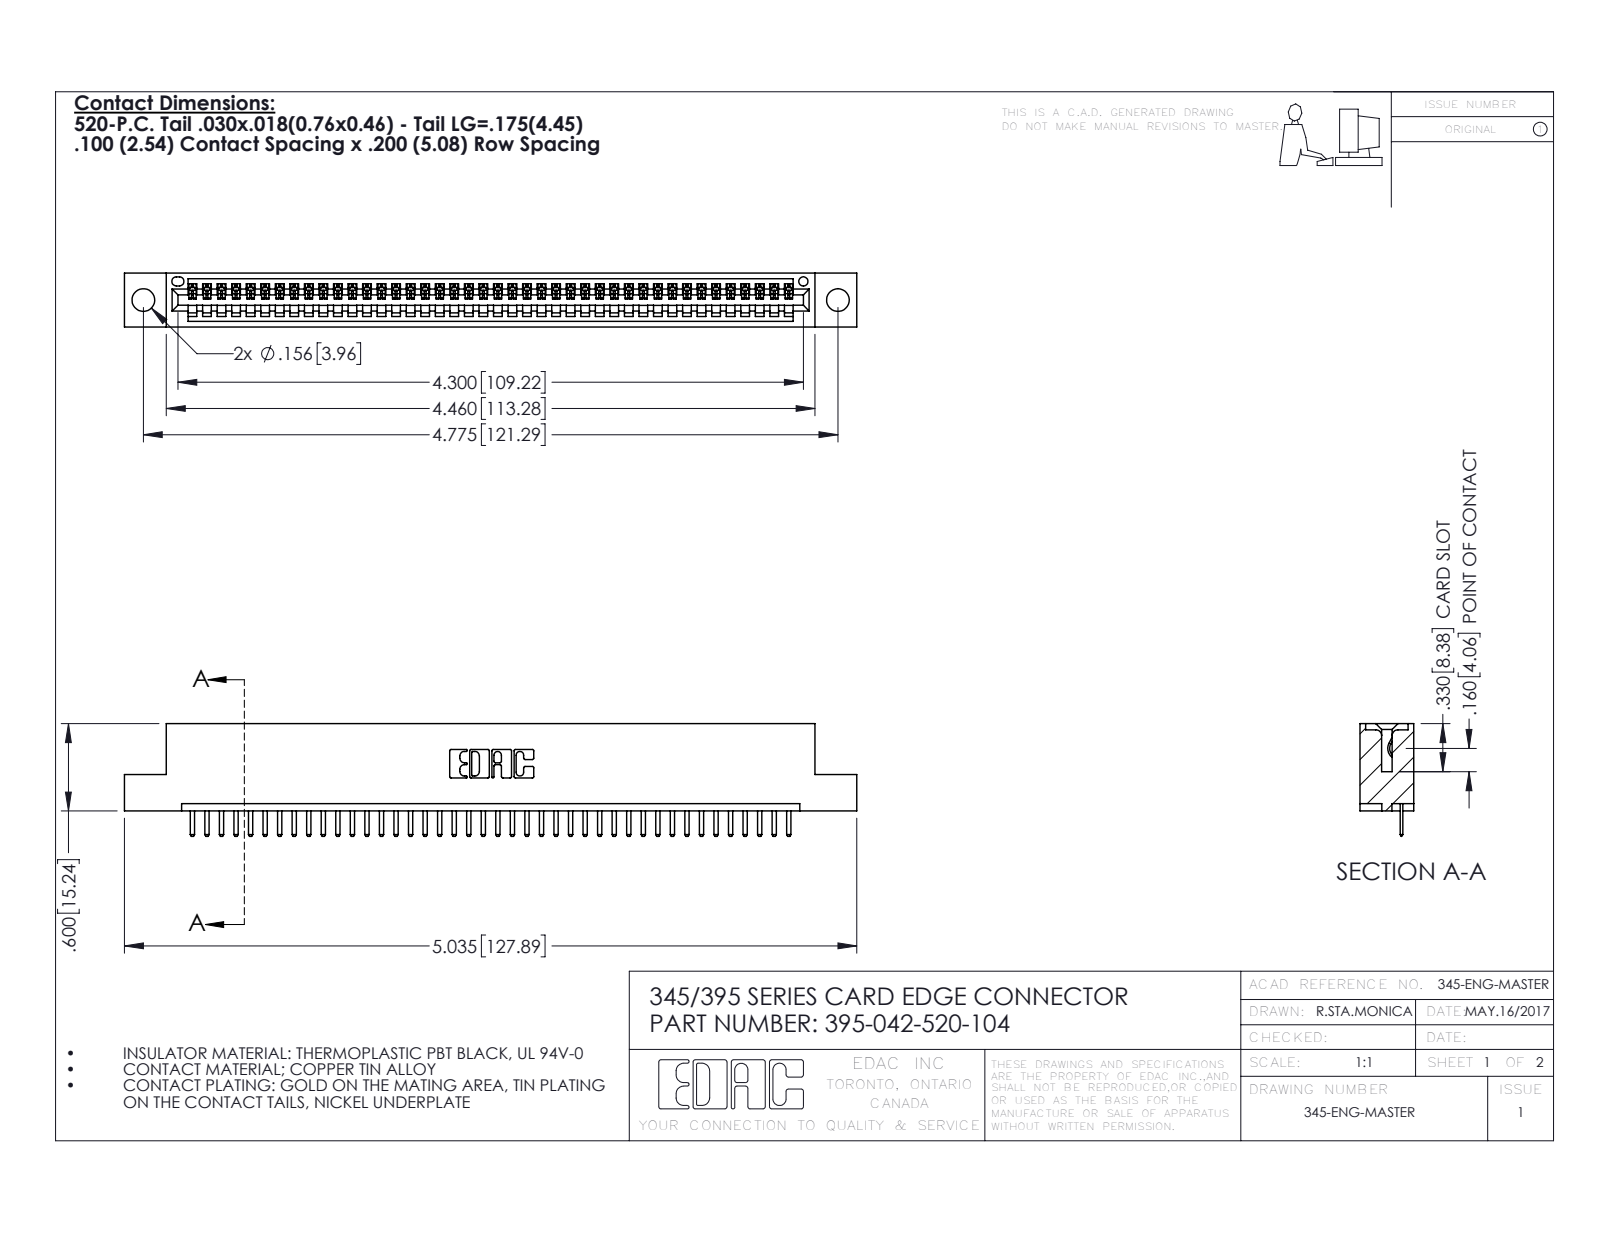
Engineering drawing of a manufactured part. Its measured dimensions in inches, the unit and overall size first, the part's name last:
Units: inches
Overall size (bounding box): 5.035 × 0.775 × 0.37
Round holes (diameter × count): ⌀0.156 ×2, ⌀0.064 ×1
Partial cylindrical surfaces — rounded edges, fillets, slot ends (radius × count): R0.01 ×86, R0.006 ×84, R0.01 ×22, R0.007 ×6, R0.031 ×6, R0.026 ×3, R0.031 ×2, R0.04 ×2
Main face-to-face distances: 0.298, 0.072, 0.37, 0.2, 0.098, 0.272, 0.025, 0.225, 0.072, 0.149
Hole centre spacings: 0.27, 4.539, 4.775
Volume: 0.729 in³ · Surface area: 23.68 in²
Bodies: 43 solids, 2730 faces (1844 planar, 886 cylindrical, 0 other)
Part name (STEP PRODUCT): 395-042-520-104; 345 Part_Flush Mounting Lugs - 0.156 Dia-TH; 345-292-001_345-293-120
STEP written by: SolidWorks 2016 (CONFIG_CONTROL_DESIGN)
